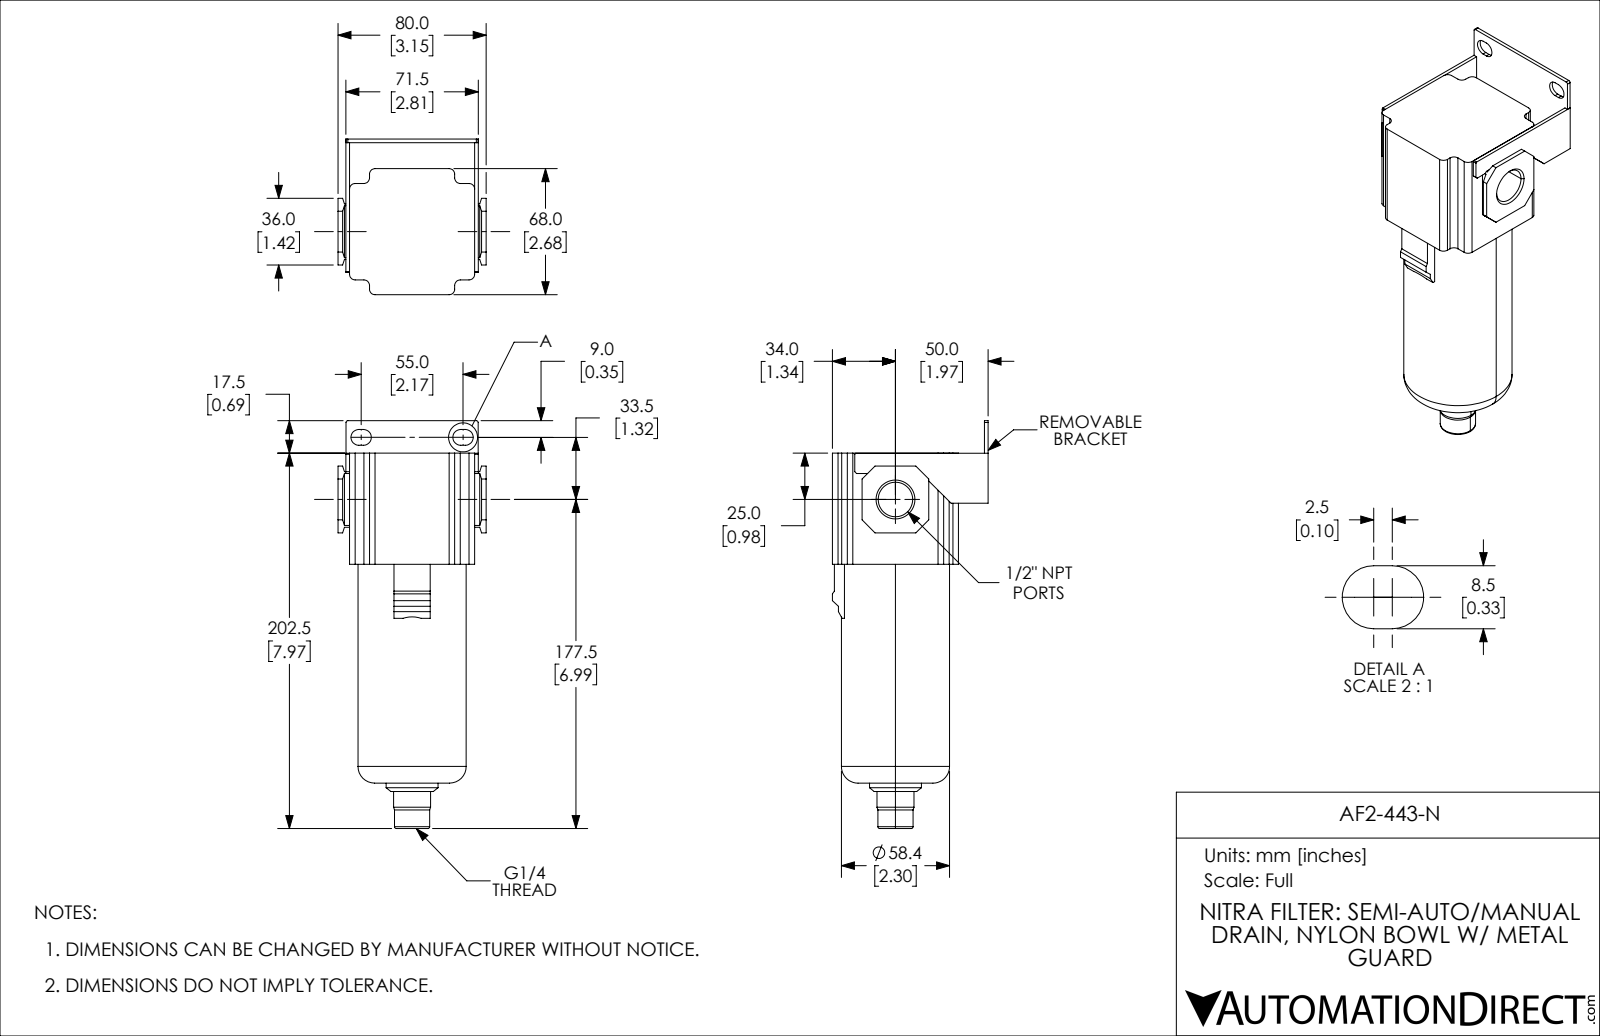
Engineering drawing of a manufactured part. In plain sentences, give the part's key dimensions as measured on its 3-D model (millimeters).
The part is named "AF2-443-N". Its 3-D file was written by "SolidWorks 2019 (CONFIG_CONTROL_DESIGN)". It is 1 solid with 136 faces: 90 planar, 32 cylindrical and 14 other. Overall it measures 220 by 84 by 80 millimeters. Its volume is 589 844 cubic millimeters and its surface area 61 015 square millimeters. Round holes: 1 of diameter 8.57, 1 of diameter 18.63. Round bosses or shafts: 1 of diameter 58.4, 1 of diameter 28, 1 of diameter 20, 1 of diameter 19. Partial cylindrical surfaces (rounded edges, fillets, slot ends): 12 of radius 3, 4 of radius 4.25, 2 of radius 1. The main face-to-face distances are 2, 16, 60, 68, 84, 82, 69.5, 14, 67.5, 4.25.
